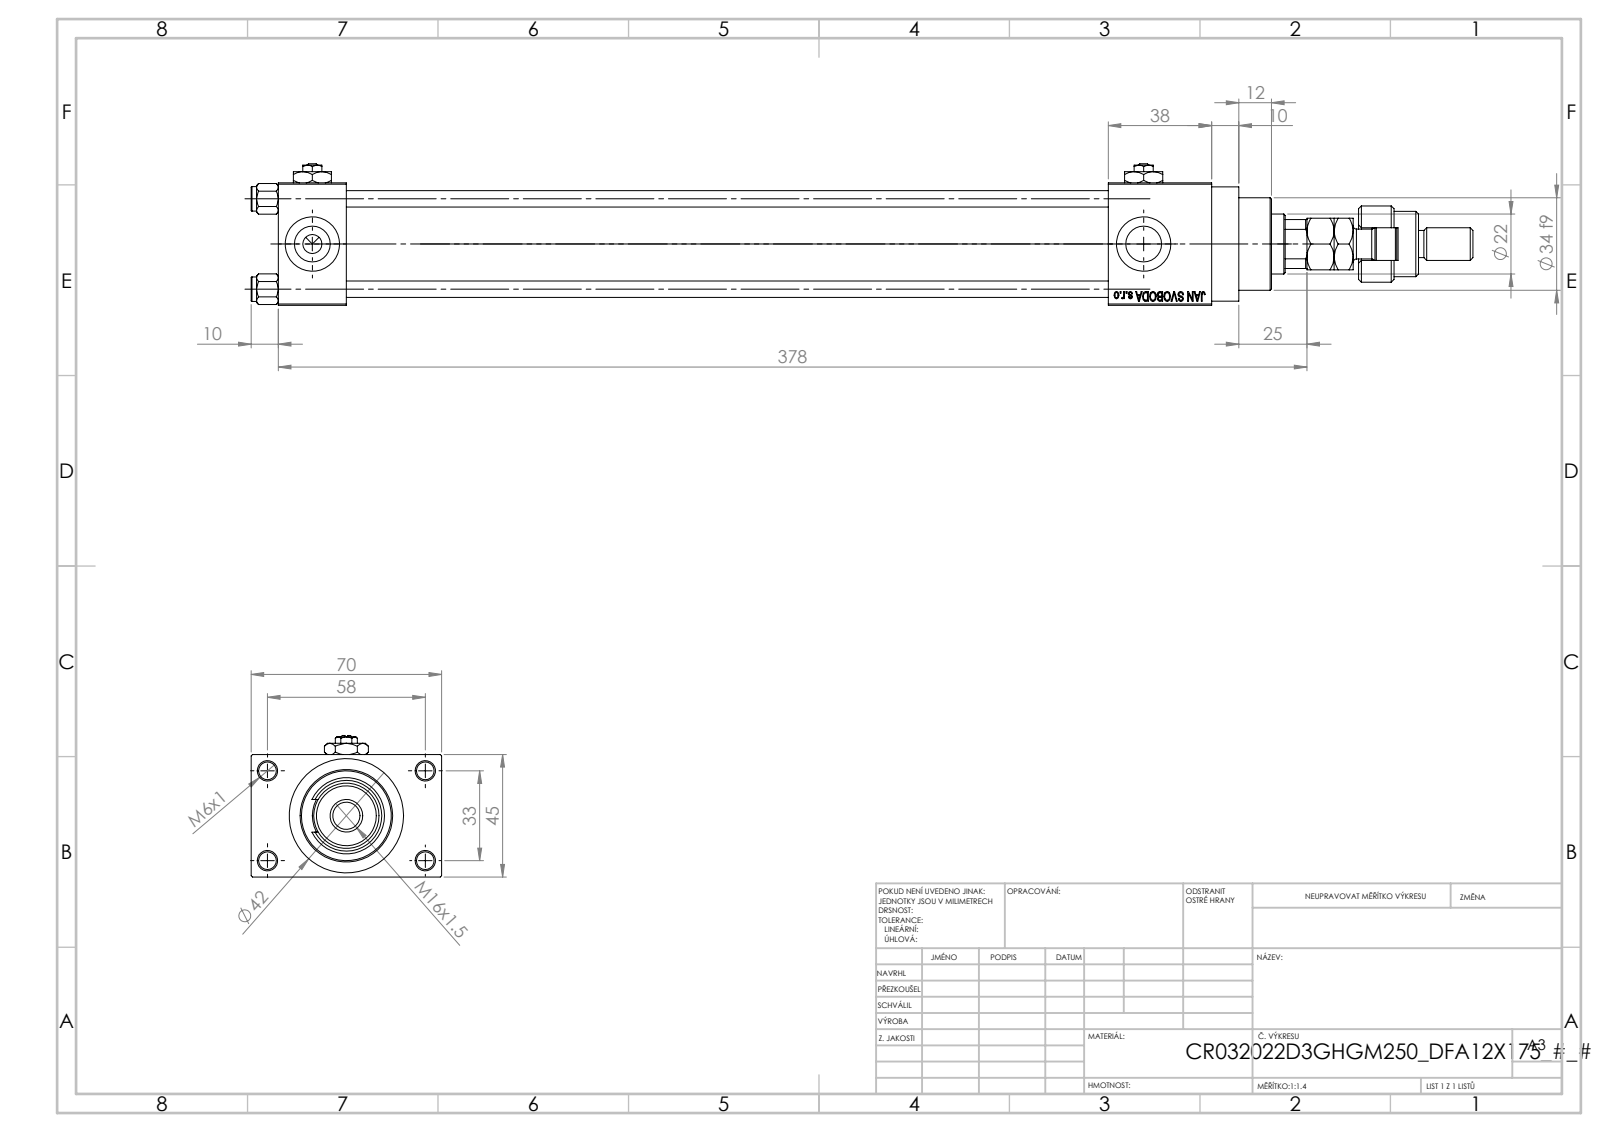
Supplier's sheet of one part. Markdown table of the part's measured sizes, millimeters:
| quantity | value |
| --- | --- |
| part name | V215_VC_A; V215CR_D_Body; MFA; Zatka_pro_OIL_PORT (+4 more) |
| STEP written by | SolidWorks 2019 (CONFIG_CONTROL_DESIGN) |
| units | millimeters |
| bodies | 15 solids, 1286 faces (570 planar, 112 cylindrical, 604 other) |
| overall size | 449 × 70 × 52 |
| volume | 448 937 mm³ |
| surface area | 172 651 mm² |
| round holes (diameter × count) | 6 × 4, 6.5 × 4, 13.16 × 4, 20 × 4, 7 × 3, 10.5 × 1, 22 × 1, 24 × 1, 25 × 1, 32 × 1, 33 × 1 |
| round bosses / shafts (diameter × count) | 9 × 4, 42 × 1, 38 × 1, 34 × 1, 28 × 1, 18 × 1, 12 × 1, 11 × 1 |
| partial cylindrical surfaces (radius × count) | 9.75 × 1, 10.5 × 1 |
| main face-to-face distances | 45, 25, 12.5, 280, 305, 57.5, 38, 318, 343, 70 |
| hole center spacings | 12.4, 23.48, 33.2, 33.37, 35.35, 45.6, 56.35, 33 |
